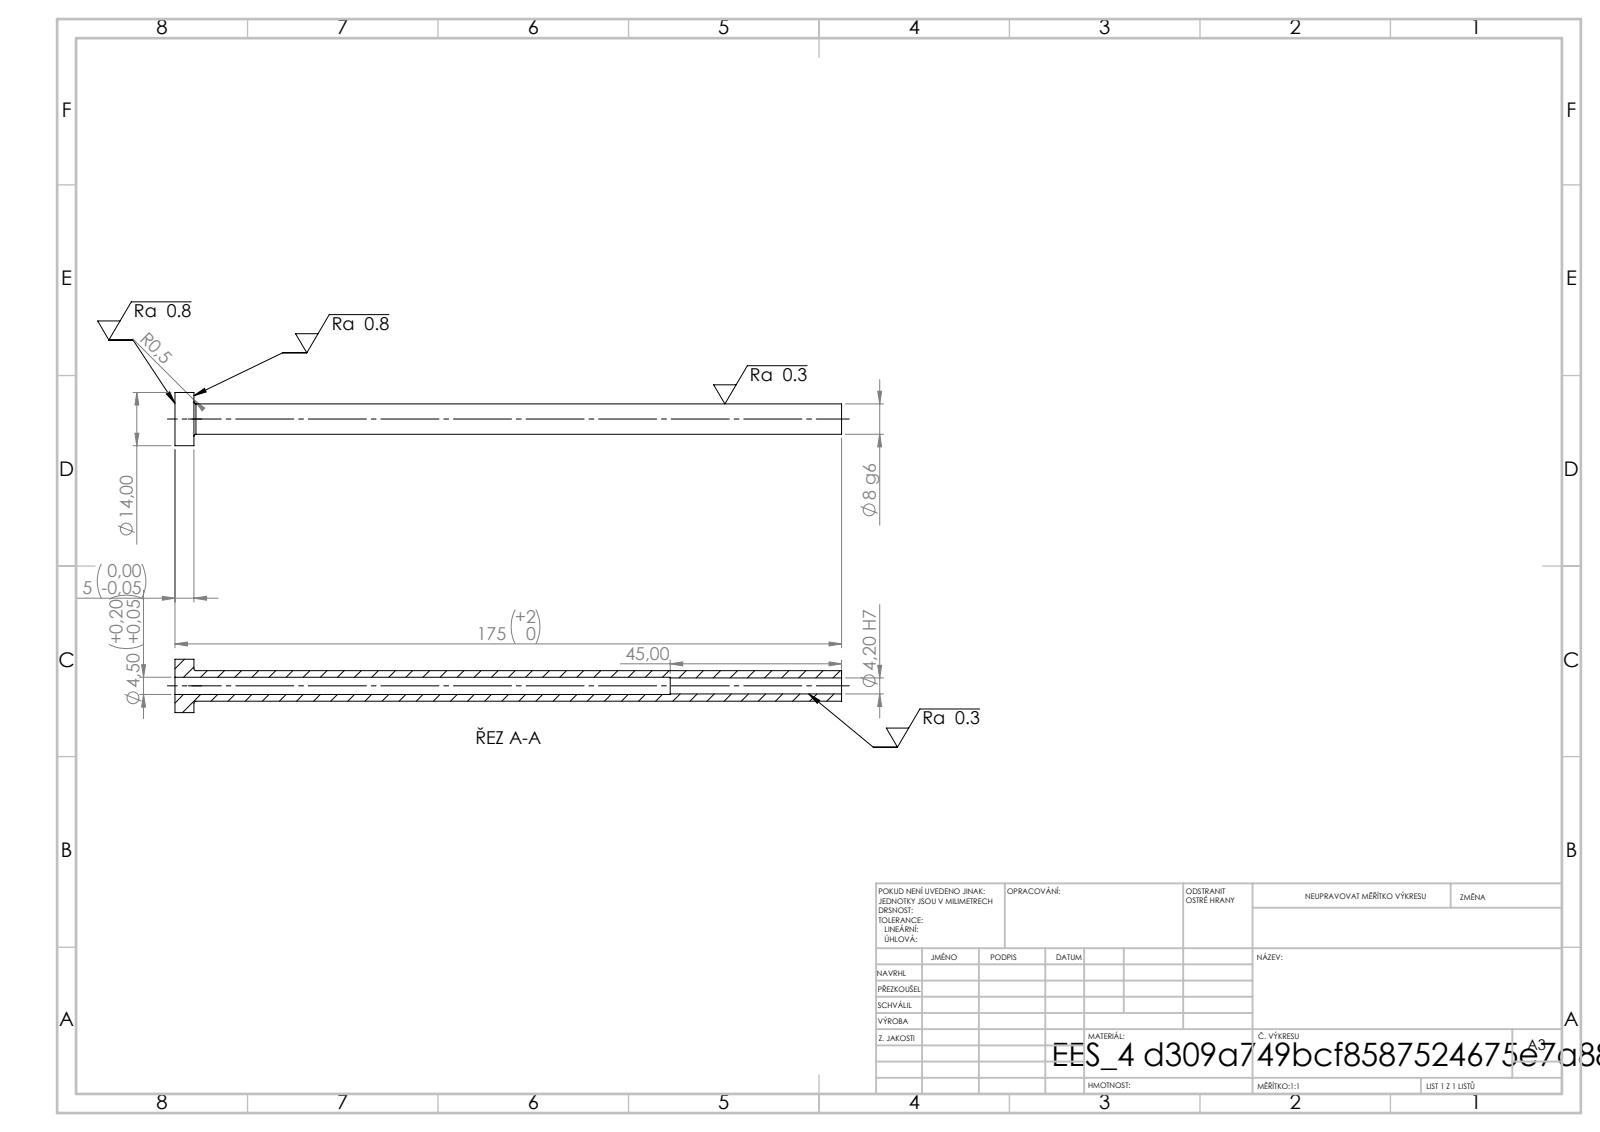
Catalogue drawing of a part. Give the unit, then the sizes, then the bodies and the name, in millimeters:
Units: millimetres
Overall size (bounding box): 175 × 14 × 14
Round holes (diameter × count): ⌀4.2 ×1, ⌀4.5 ×1
Round bosses / shafts (diameter × count): ⌀14 ×1, ⌀8 ×1
Main face-to-face distances: 5, 175, 170, 130, 125, 45
Volume: 6 625 mm³ · Surface area: 7 199 mm²
Bodies: 1 solid, 14 faces (4 planar, 8 cylindrical, 2 other)
STEP written by: SolidWorks 2019 (CONFIG_CONTROL_DESIGN)
